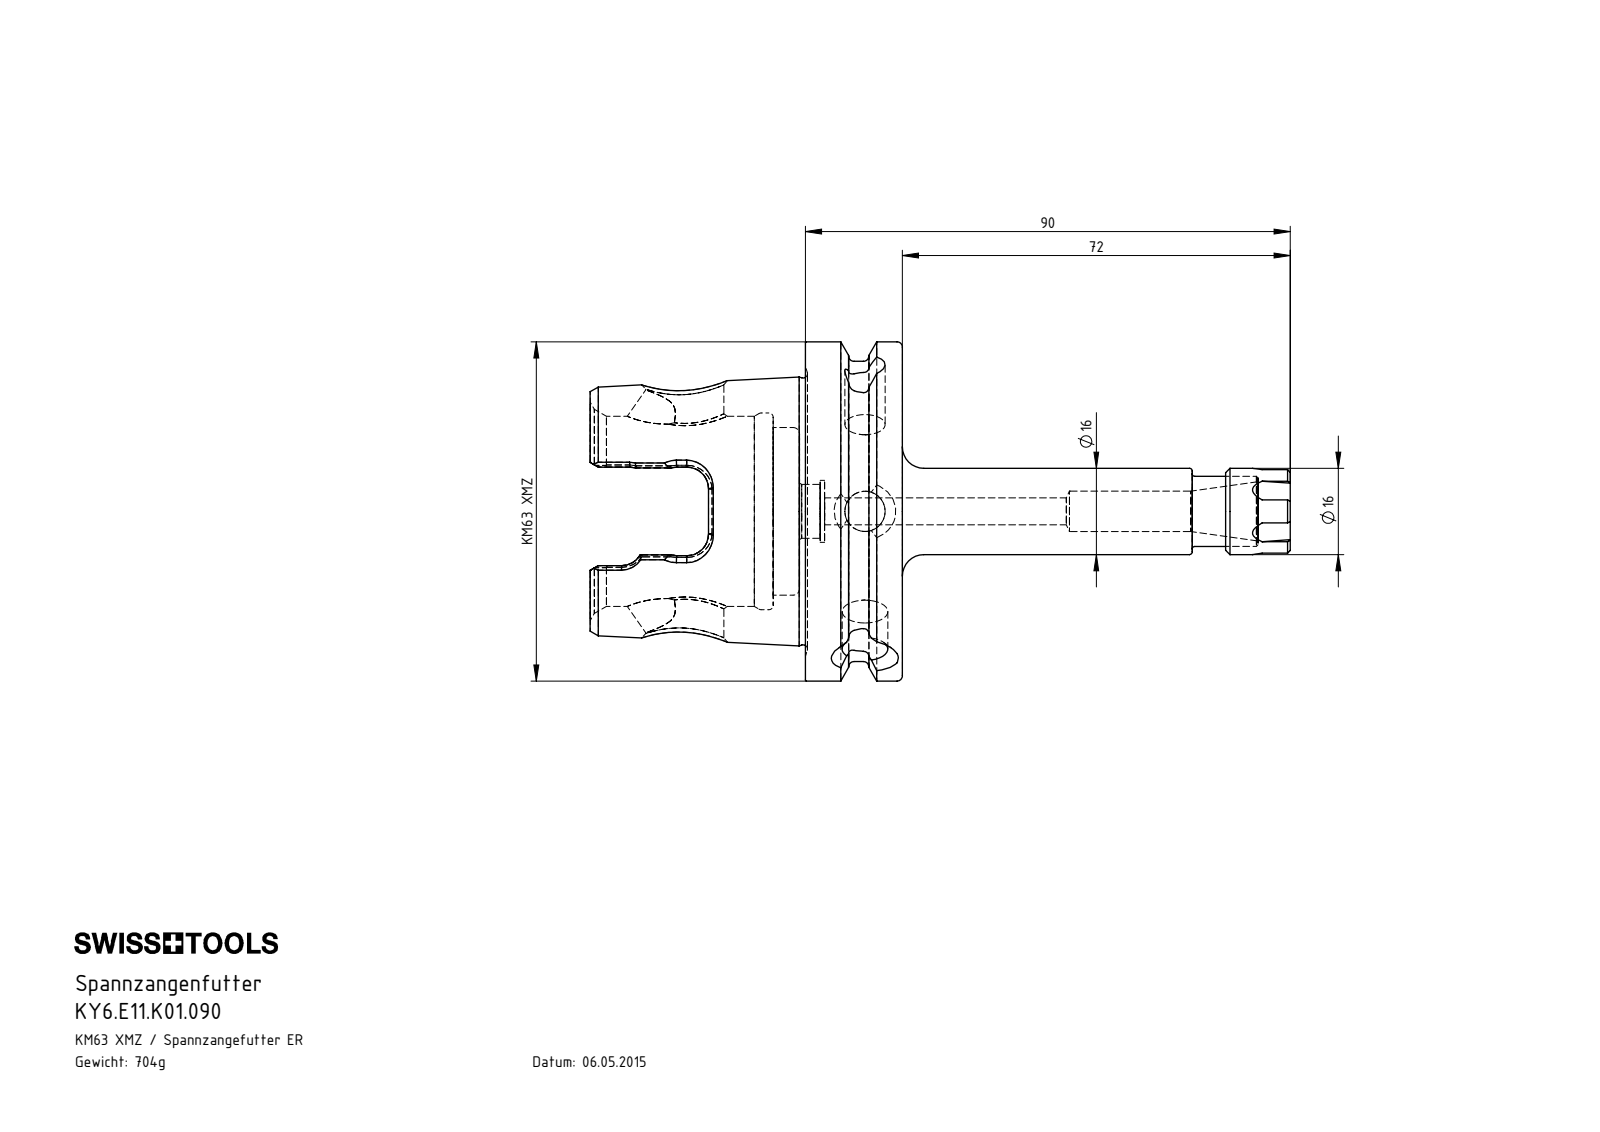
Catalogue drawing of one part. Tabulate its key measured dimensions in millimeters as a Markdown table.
| quantity | value |
| --- | --- |
| part name | KY6-E11.K01.090; ERU-AN2.K01.016_A; E11-ER1.001.012; KY6-E11.K01.090_B |
| STEP written by | SolidWorks 2012 (CONFIG_CONTROL_DESIGN) |
| units | millimeters |
| bodies | 3 solids, 316 faces (101 planar, 69 cylindrical, 146 other) |
| overall size | 129.95 × 62.95 × 62.95 |
| volume | 89 656 mm³ |
| surface area | 26 200 mm² |
| round holes (diameter × count) | 7.47 × 2, 3 × 1, 5 × 1, 7.5 × 1, 8.48 × 1, 10 × 1, 11.5 × 1, 11.7 × 1, 12.4 × 1, 13.5 × 1, 14.5 × 1, 15.5 × 1 |
| round bosses / shafts (diameter × count) | 62.95 × 1, 55.7 × 1, 16 × 1, 13 × 1, 6 × 1 |
| partial cylindrical surfaces (radius × count) | 4 × 6, 7.04 × 2 |
| main face-to-face distances | 18, 1.1, 19.1, 6, 4.9, 24, 33.95, 38.85, 39.95, 57.95 |
